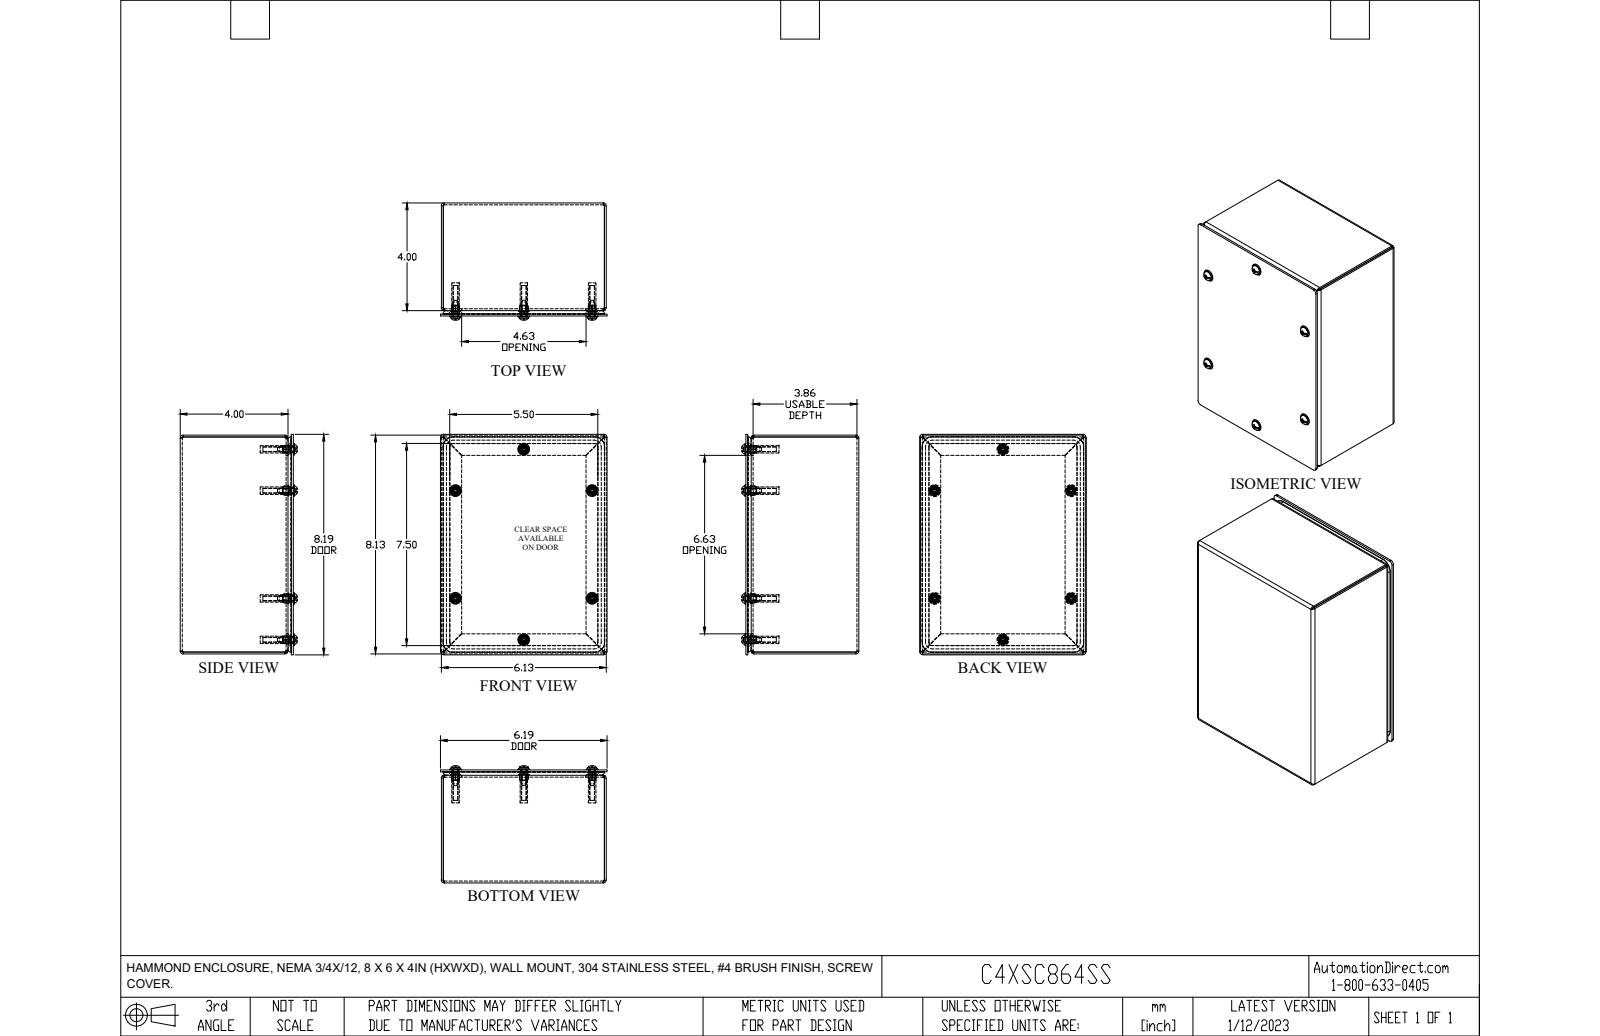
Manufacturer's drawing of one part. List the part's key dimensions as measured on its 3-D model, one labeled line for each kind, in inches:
Part name (STEP PRODUCT): C3SC864GY
STEP written by: SolidWorks 2021 (AUTOMOTIVE_DESIGN)
Units: inches
Bodies: 21 solids, 606 faces (370 planar, 122 cylindrical, 114 other)
Overall size (bounding box): 8.188 × 6.188 × 4.347
Volume: 16.96 in³ · Surface area: 504.5 in²
Round holes (diameter × count): ⌀0.159 ×6, ⌀0.16 ×6, ⌀0.25 ×6
Round bosses / shafts (diameter × count): ⌀0.44 ×6, ⌀0.39 ×6, ⌀0.24 ×6, ⌀0.19 ×6, ⌀0.148 ×6, ⌀0.275 ×4, ⌀0.275 ×2
Partial cylindrical surfaces — rounded edges, fillets, slot ends (radius × count): R0.04 ×8, R0.11 ×8, R0.125 ×8, R0.16 ×6, R0.126 ×4, R0.374 ×4
Main face-to-face distances: 0.07, 0.07, 0.072, 4.127, 4.197, 4.055, 4.125, 3.93, 6.13, 6.06
Hole centre spacings: 2.967, 6.091, 4, 5.075, 6.462, 7.075
